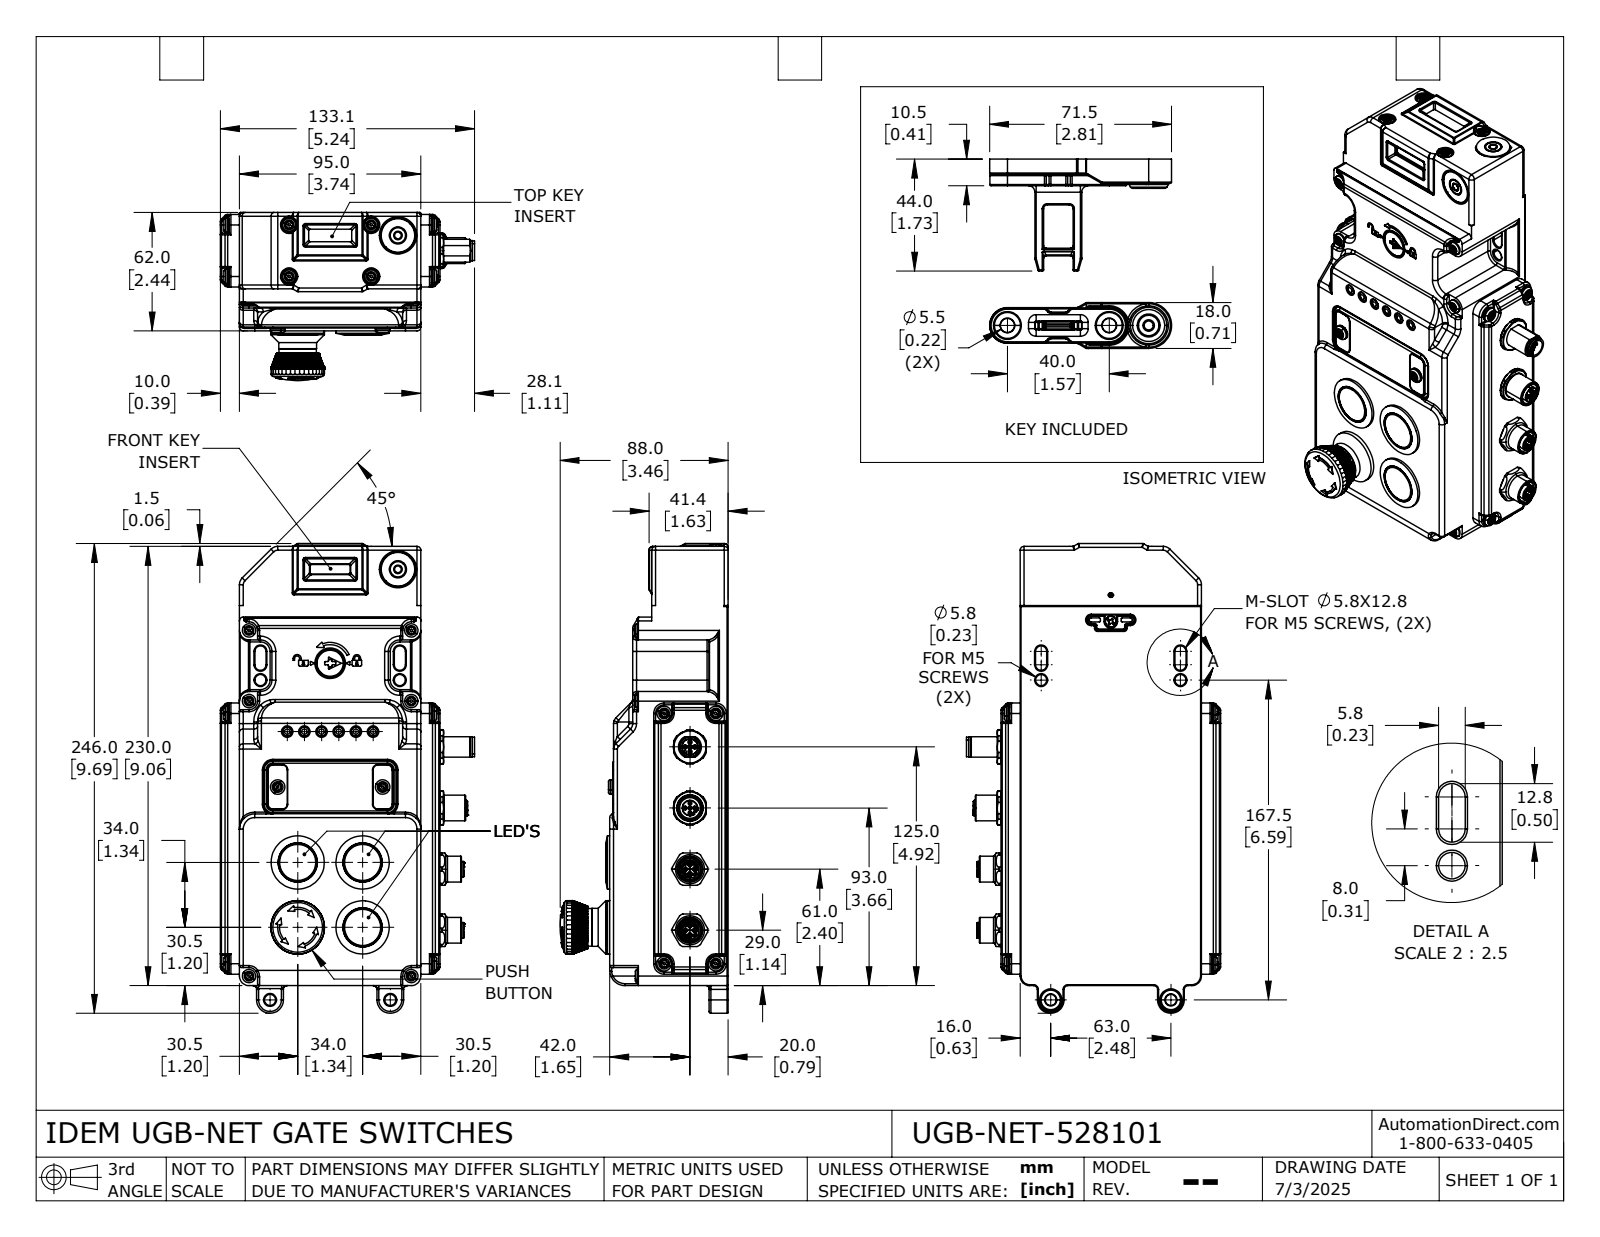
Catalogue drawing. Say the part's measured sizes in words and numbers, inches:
The part is named "UGB-NET-528101". Its 3-D file was written by "SolidWorks 2024 (AUTOMOTIVE_DESIGN)". It is 7 solids with 4287 faces: 1254 planar, 1630 cylindrical and 1403 other. Overall it measures 10.217 by 5.24 by 3.465 inches. Its volume is 78.9 cubic inches and its surface area 189.1 square inches. Round holes: 8 of diameter 0.049, 8 of diameter 0.077, 8 of diameter 0.177, 7 of diameter 0.087, 6 of diameter 0.157, 6 of diameter 0.197, 5 of diameter 0.043, 5 of diameter 0.098, 4 of diameter 0.228, 4 of diameter 0.315, 3 of diameter 0.134, 2 of diameter 0.138. Round bosses or shafts: 16 of diameter 0.051, 8 of diameter 0.189, 7 of diameter 0.039, 6 of diameter 0.299, 6 of diameter 0.276, 5 of diameter 0.079, 4 of diameter 0.256, 3 of diameter 1.098. Partial cylindrical surfaces (rounded edges, fillets, slot ends): 223 of radius 0.039, 206 of radius 0.02, 129 of radius 0.008, 74 of radius 0.079, 46 of radius 0.012, 40 of radius 0.031, 14 of radius 0.016, 14 of radius 0.098. The main face-to-face distances are 0.394, 4.134, 2.441, 3.74, 0.472, 1.535, 0.079, 0.039, 0.059, 4.528. The hole center spacings are 0.098, 0.139, 0.197, 1.063, 1.264, 1.26, 2.52, 2.522.
